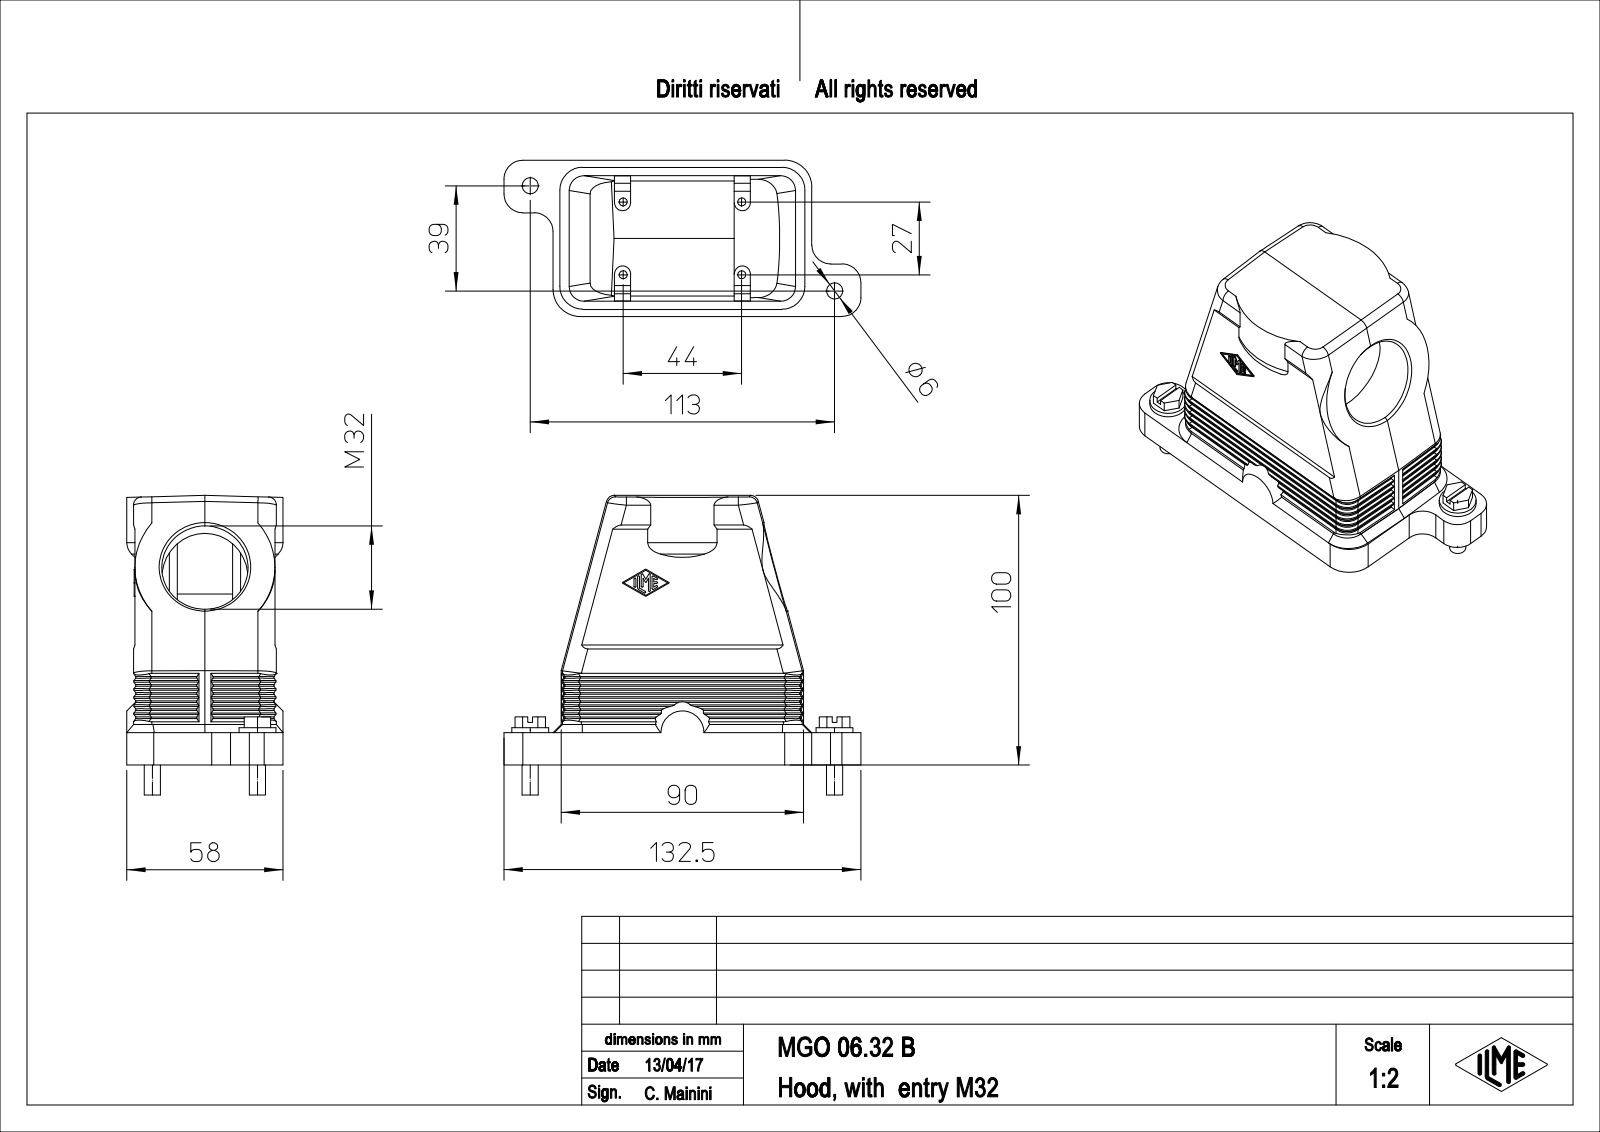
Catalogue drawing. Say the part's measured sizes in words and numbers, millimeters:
The part is named "MGO_06.32_B". Its 3-D file was written by "PTC Creo Elements/Direct Modeling 19.0E 27-Jun-2016 (C) Parametric Technology GmbH (AUTOMOTIVE_DESIGN)". It is 1 solid with 523 faces: 249 planar, 210 cylindrical and 64 other. Overall it measures 132.5 by 111.2 by 58 millimeters. Its volume is 141 704 cubic millimeters and its surface area 63 369 square millimeters. Round holes: 4 of diameter 3, 1 of diameter 32. Round bosses or shafts: 2 of diameter 13.7, 2 of diameter 6, 2 of diameter 2. Partial cylindrical surfaces (rounded edges, fillets, slot ends): 66 of radius 0.5, 62 of radius 7, 15 of radius 0.33, 6 of radius 3, 4 of radius 5.5, 4 of radius 8.5, 3 of radius 0.17, 2 of radius 10. The main face-to-face distances are 3, 55, 52, 2.5, 6, 44.5, 3.33, 0.5, 55.5, 52.5. The hole center spacings are 27, 44, 51.62.
